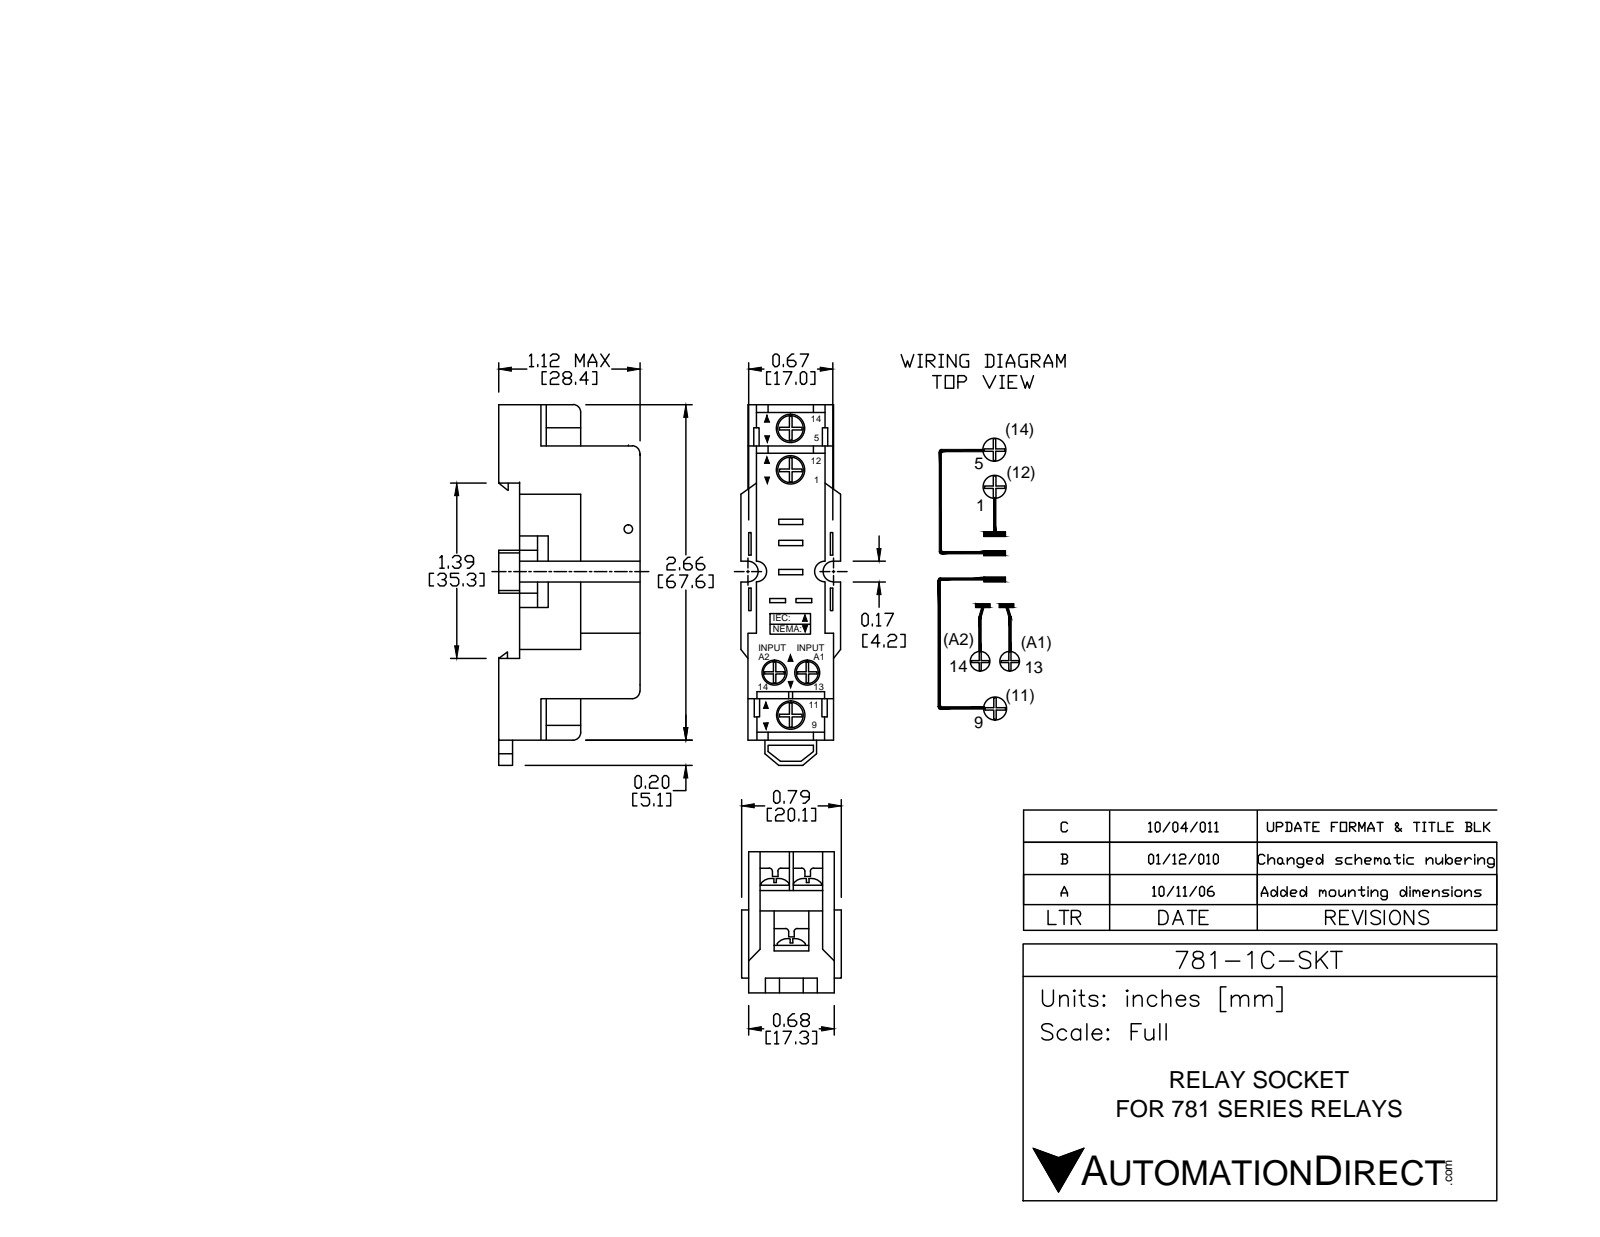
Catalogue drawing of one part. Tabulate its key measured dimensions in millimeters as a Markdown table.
| quantity | value |
| --- | --- |
| part name | 781-1C-SKT |
| STEP written by | SolidWorks 2013 (AUTOMOTIVE_DESIGN) |
| units | millimeters |
| bodies | 1 solid, 248 faces (220 planar, 28 cylindrical, 0 other) |
| overall size | 72.6 × 28.4 × 20.1 |
| volume | 24 470 mm³ |
| surface area | 8 394 mm² |
| round holes (diameter × count) | 5.6 × 5 |
| partial cylindrical surfaces (radius × count) | 1.5 × 4, 2.2 × 2, 2.2 × 2, 3.3 × 2 |
| main face-to-face distances | 1.8, 15.5, 16.9, 1.4, 3.2, 18.7, 24.1, 17.3, 4.3, 15 |
| hole center spacings | 9.2, 40.8, 49.3, 7.1, 8.5, 49.1, 57.6 |
